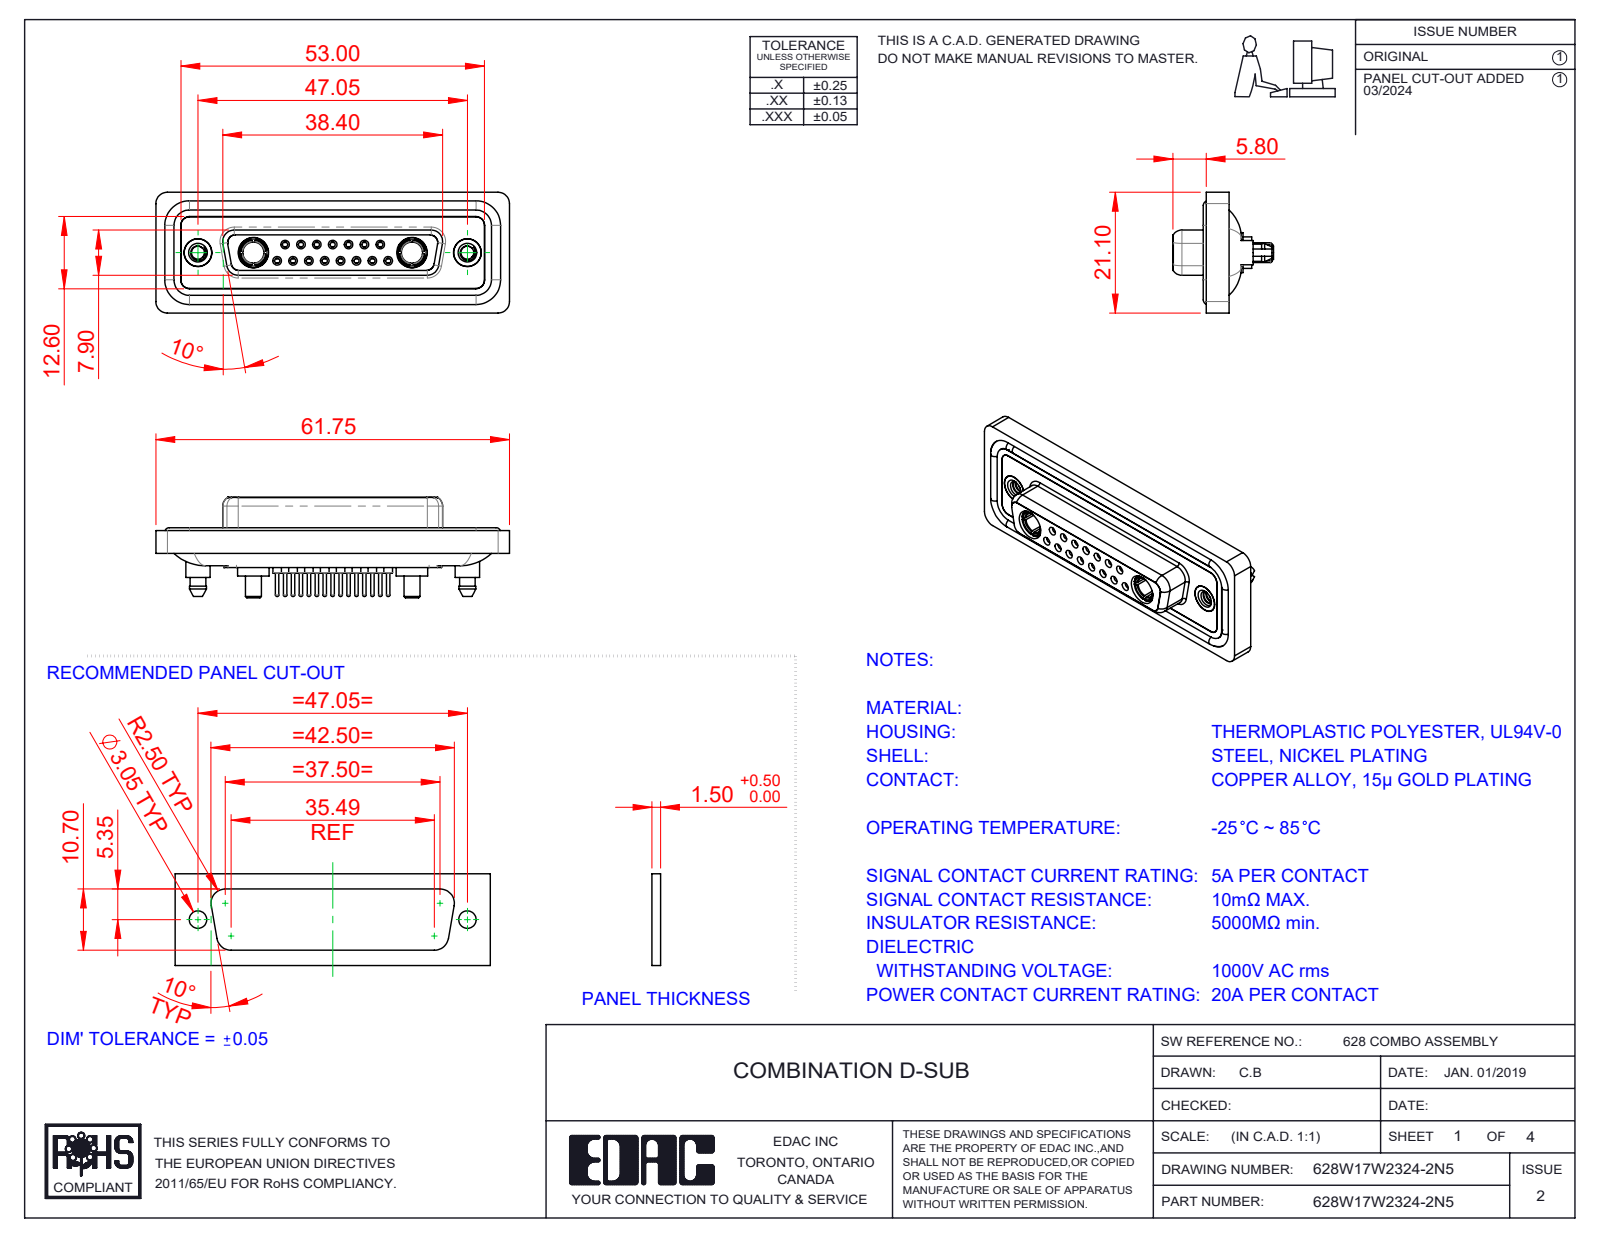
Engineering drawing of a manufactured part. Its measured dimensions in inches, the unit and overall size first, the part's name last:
Units: inches
Overall size (bounding box): 2.431 × 0.831 × 0.691
Round holes (diameter × count): ⌀0.035 ×15, ⌀0.043 ×15, ⌀0.059 ×15, ⌀0.079 ×15, ⌀0.063 ×8, ⌀0.067 ×7, ⌀0.191 ×4, ⌀0.089 ×2, ⌀0.146 ×2, ⌀0.157 ×2, ⌀0.159 ×2, ⌀0.197 ×2
Round bosses / shafts (diameter × count): ⌀0.087 ×15, ⌀0.024 ×15, ⌀0.063 ×11, ⌀0.217 ×2, ⌀0.213 ×2, ⌀0.205 ×2, ⌀0.195 ×2, ⌀0.195 ×2
Partial cylindrical surfaces — rounded edges, fillets, slot ends (radius × count): R0.059 ×24, R0.079 ×18, R0.063 ×10, R0.053 ×8, R0.01 ×4, R0.02 ×4, R0.024 ×4, R0.026 ×4
Main face-to-face distances: 0.016, 0.071, 0.293, 0.222, 0.26, 0.02, 0.278, 0.063, 0.114, 0.043
Hole centre spacings: 0.124, 0.109, 0.327, 0.218, 0.198, 0.198, 0.295, 0.436
Volume: 0.516 in³ · Surface area: 21.99 in²
Bodies: 26 solids, 1409 faces (404 planar, 551 cylindrical, 454 other)
Part name (STEP PRODUCT): 628Combo Contact Row 2_24; 628Combo Shell Rear_25 Contacts; 628Combo Threaded Boardlock_5; 628Combo Housing_17W2 (+5 more)
STEP written by: SolidWorks 2023 (CONFIG_CONTROL_DESIGN)
